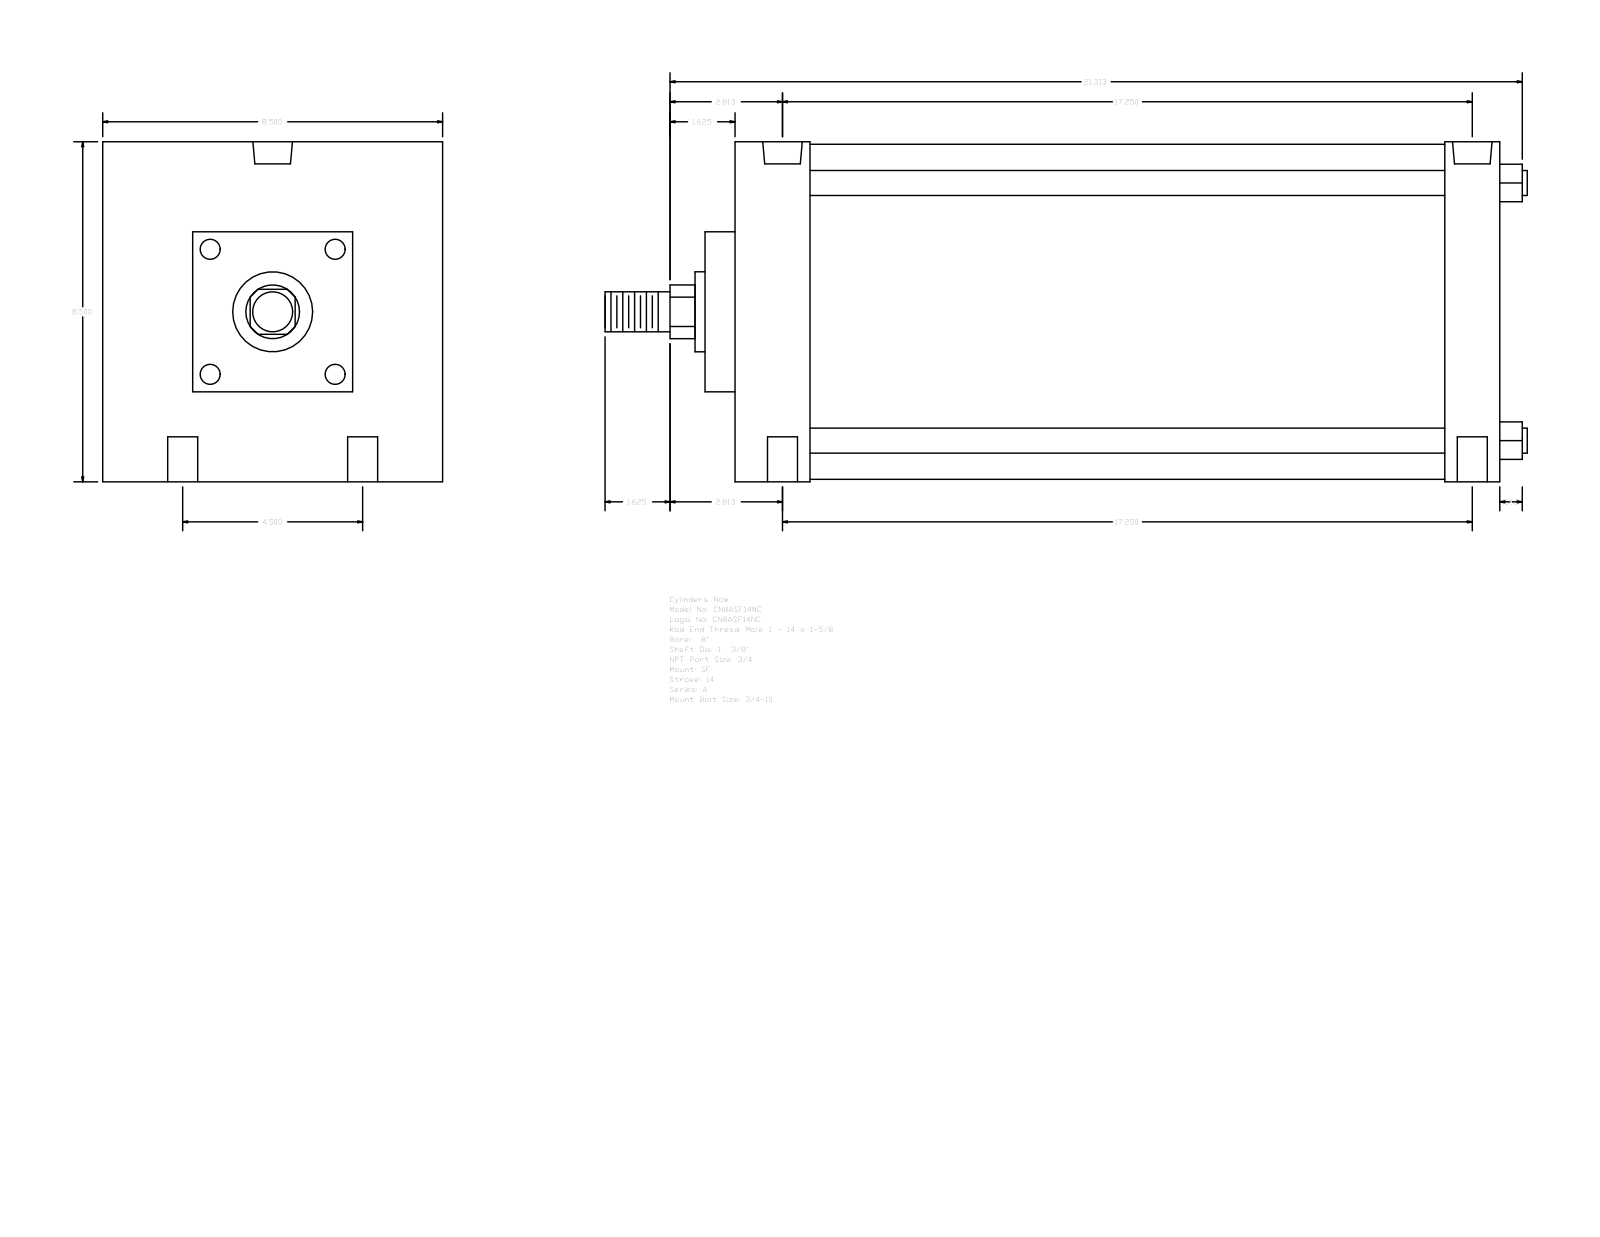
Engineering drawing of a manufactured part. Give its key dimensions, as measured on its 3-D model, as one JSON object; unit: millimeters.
{"part_name": "A_SF__0800_1.375", "step_written_by": "GSSL Pune (CONFIG_CONTROL_DESIGN)", "units": "millimeters", "bodies": {"solids": 0, "faces": 93, "planar": 67, "cylindrical": 26, "other": 0}, "overall_size": [585.79, 215.9, 215.9], "round_holes": [[19.05, 4], [15.08, 2], [25.12, 2]], "round_bosses_or_shafts": [[15.88, 4], [212.72, 1], [50.8, 1], [34.92, 1], [25.4, 1]], "partial_cylinders_radius": [[17.06, 1]], "face_to_face_distances": [485.78, 215.9, 47.63, 450.85, 403.22, 438.15, 34.93, 19.04, 66.67, 469.89], "hole_center_spacings": [57.15, 441.86, 438.15, 114.3, 452.81, 425.45]}
